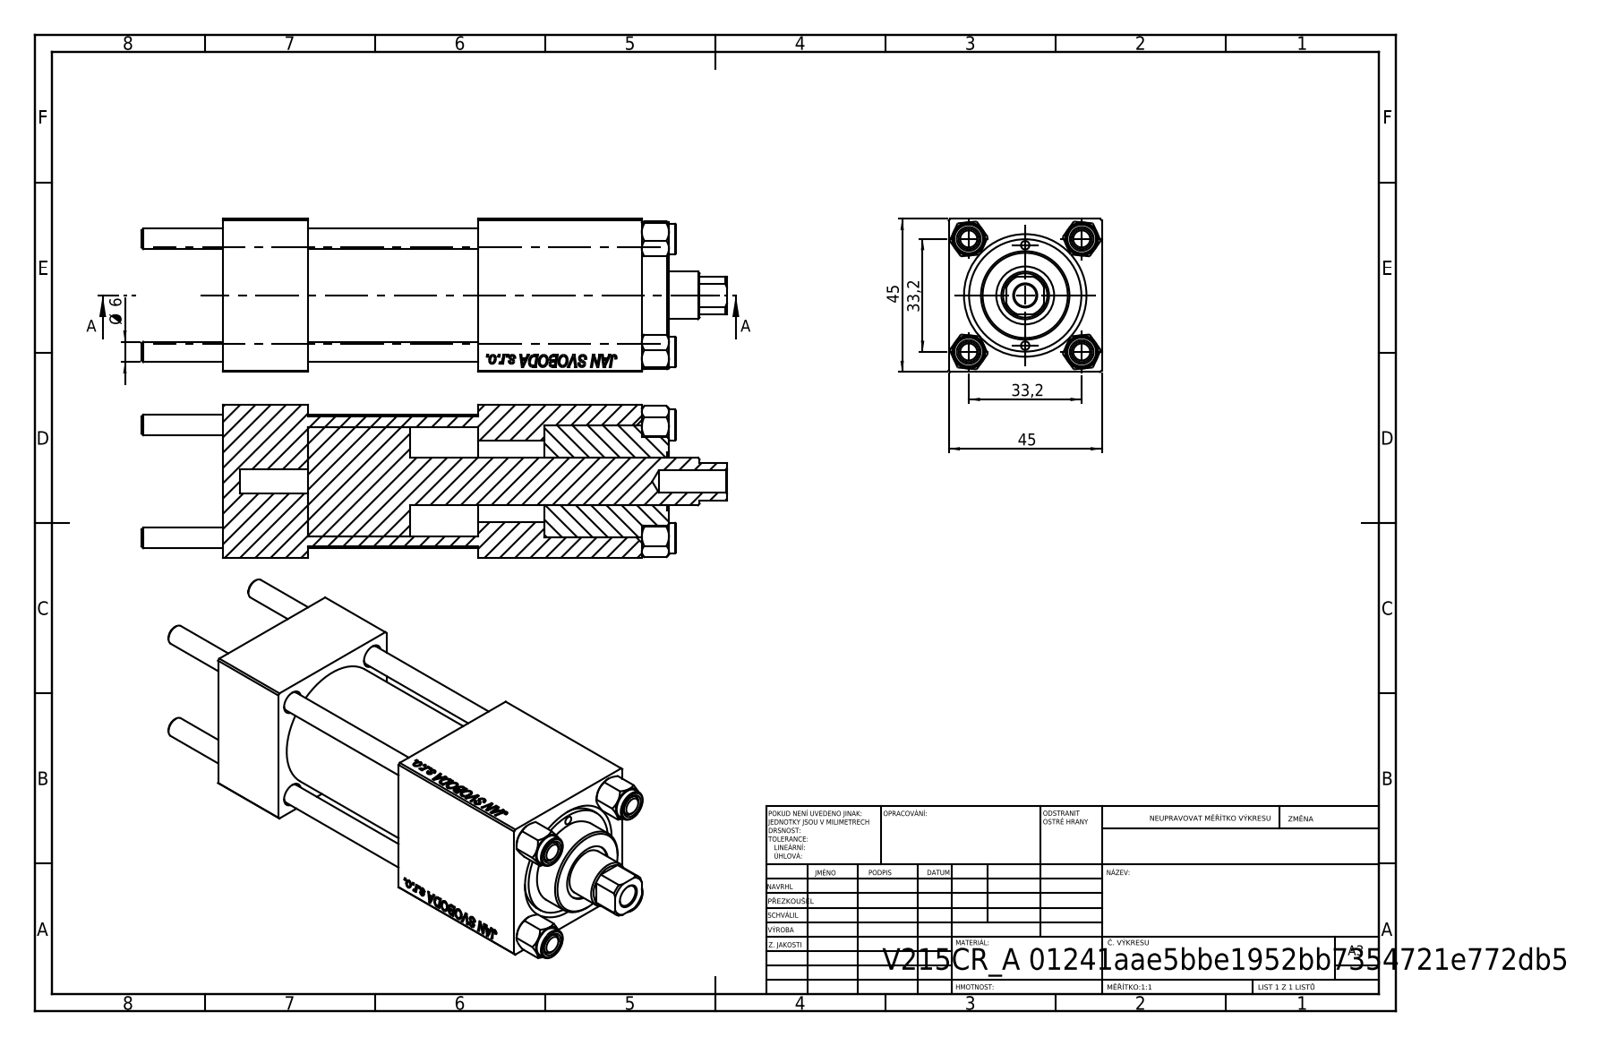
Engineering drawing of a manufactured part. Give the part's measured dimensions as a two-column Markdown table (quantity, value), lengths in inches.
| quantity | value |
| --- | --- |
| part name | CR025_012_A_0_G_A_G_M_020_+#_##_TYCINKA; V215CR_VCP; V215CR_BODY_A; NUT_M5 (+1 more) |
| STEP written by | SolidWorks 2019 (CONFIG_CONTROL_DESIGN) |
| units | inches |
| bodies | 11 solids, 1139 faces (521 planar, 82 cylindrical, 536 other) |
| overall size | 6.772 × 1.772 × 1.772 |
| volume | 12.1 in³ |
| surface area | 113 in² |
| round holes (diameter × count) | 0.236 × 4, 0.098 × 2, 0.276 × 2, 0.518 × 2, 0.787 × 2, 0.256 × 1, 0.551 × 1, 0.669 × 1, 0.945 × 1, 1.26 × 1, 1.299 × 1 |
| round bosses / shafts (diameter × count) | 0.354 × 4, 1.496 × 1, 1.024 × 1 |
| partial cylindrical surfaces (radius × count) | 0.256 × 1 |
| main face-to-face distances | 1.772, 0.984, 4.843, 3.858, 1.969, 2.953, 1.89, 3.713, 2.728, 0.76 |
| hole center spacings | 0.657, 0.924, 1.307, 1.396, 0.581, 1.848, 1.161, 2.972 |
